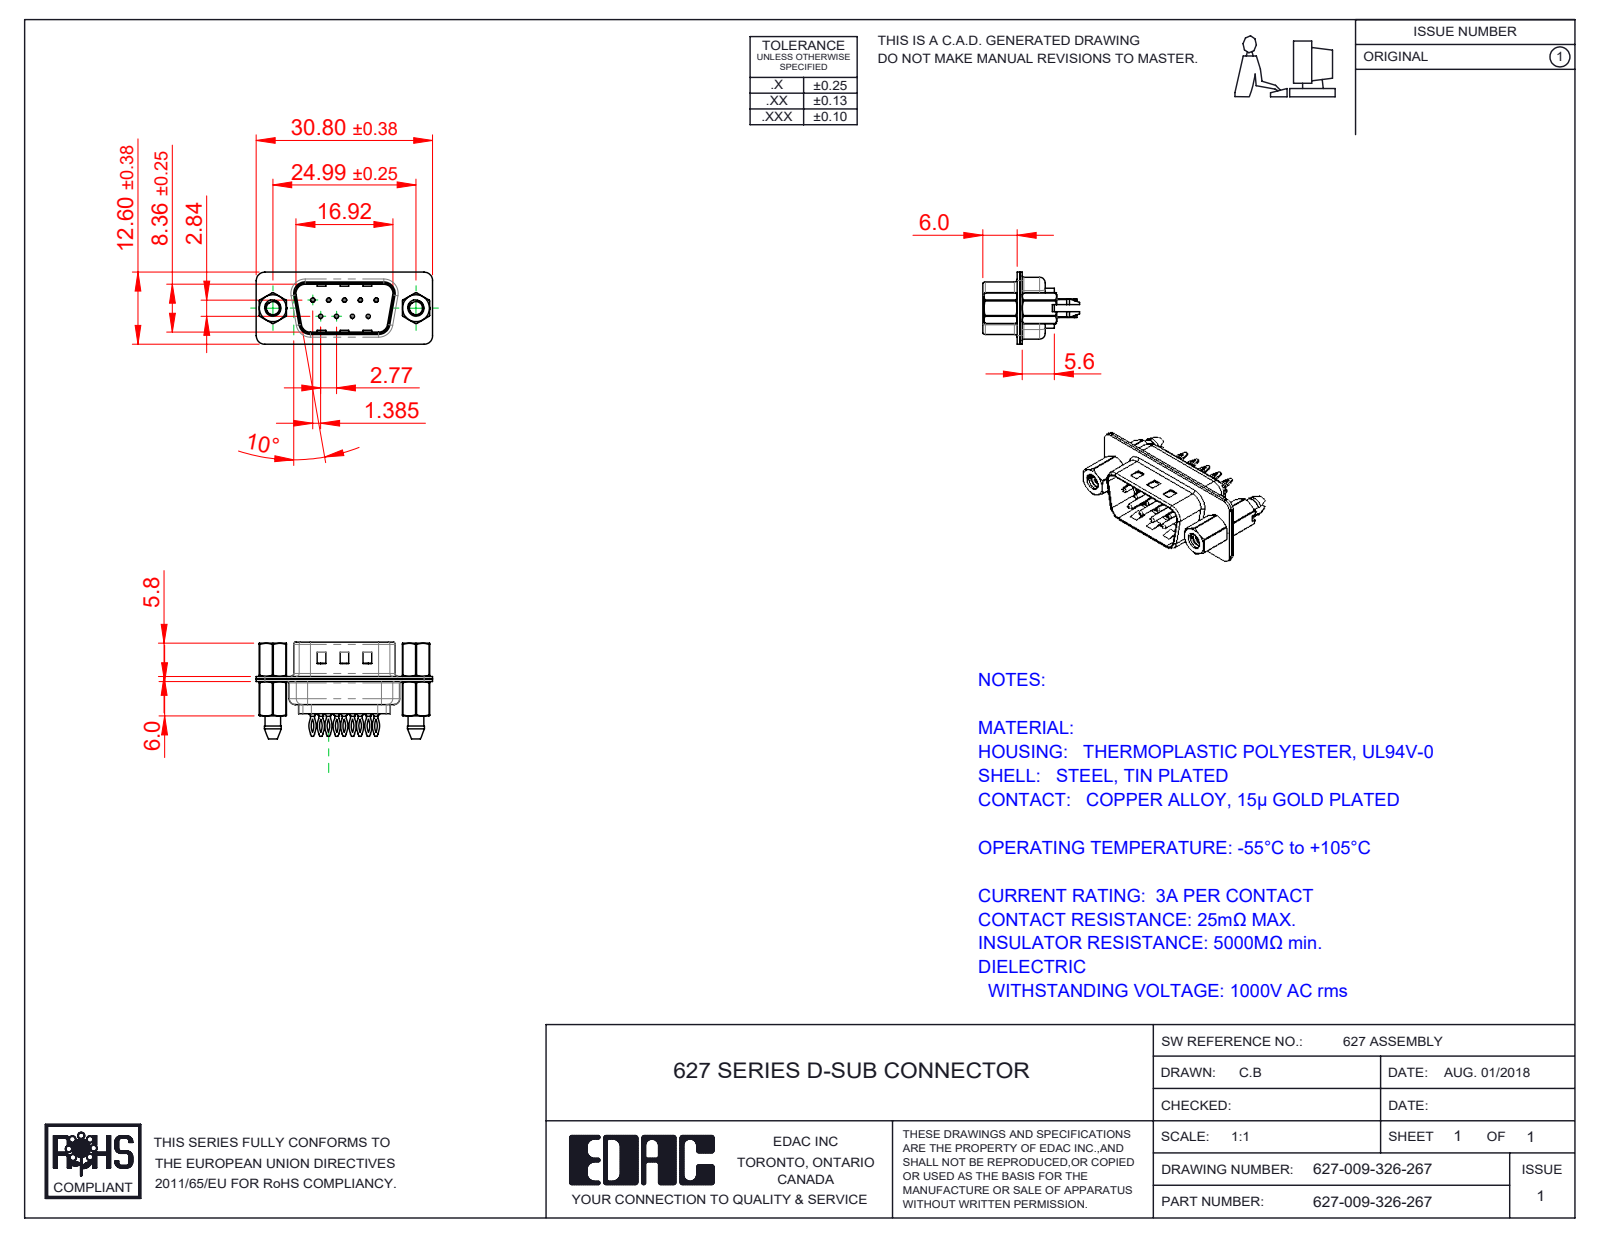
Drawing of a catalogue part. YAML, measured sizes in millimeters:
part_name: "627 Shell Rear_09 Contacts; 627 Contact Row 2_26L; 627 Shell Front_09 Contacts; 627 Housing_09 LP (+4 more)"
step_written_by: "SolidWorks 2020 (CONFIG_CONTROL_DESIGN)"
units: millimeters
bodies: {solids: 16, faces: 1188, planar: 341, cylindrical: 512, other: 335}
overall_size: [30.8, 16.9, 12.6]
volume: 1639
surface_area: 4680
round_holes:
  - {diameter: 0.35, count: 9}
  - {diameter: 1.1, count: 9}
  - {diameter: 1.6, count: 9}
  - {diameter: 2.26, count: 2}
  - {diameter: 2.29, count: 2}
  - {diameter: 4, count: 2}
  - {diameter: 4.8, count: 2}
round_bosses_or_shafts:
  - {diameter: 2, count: 9}
  - {diameter: 1.5, count: 9}
  - {diameter: 0.75, count: 9}
  - {diameter: 4.9, count: 2}
  - {diameter: 2.79, count: 2}
partial_cylinders:
  - {radius: 1.5, count: 20}
  - {radius: 2.92, count: 18}
  - {radius: 3.33, count: 18}
  - {radius: 2, count: 12}
  - {radius: 1.6, count: 10}
  - {radius: 0.5, count: 8}
  - {radius: 0.25, count: 4}
  - {radius: 0.6, count: 4}
face_to_face_distances: [0.45, 0.4, 0.9, 0.82, 9.58, 1.4, 4.76, 8.76, 6.5, 0.5]
hole_center_spacings: [3.16, 2.77, 5.54, 5.03, 5.04, 8.31, 7.48, 7.49]
